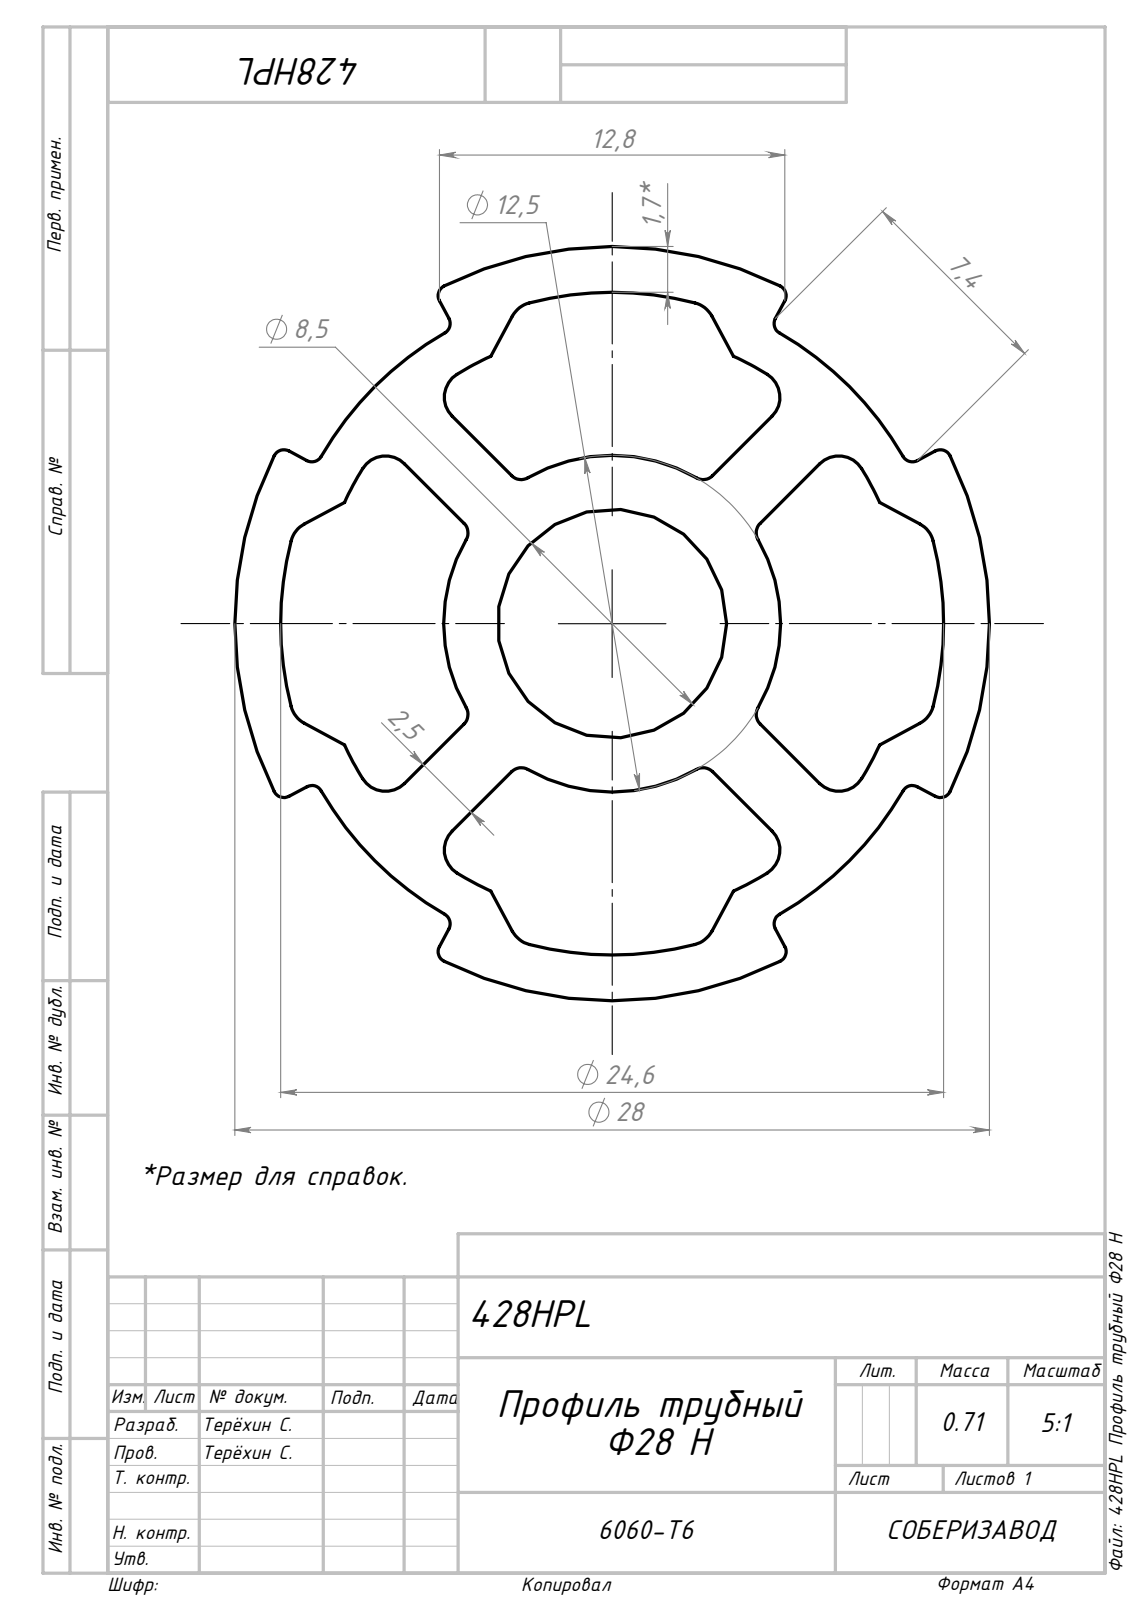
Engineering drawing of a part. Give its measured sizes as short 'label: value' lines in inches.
name: 428HPL Профиль трубный Φ28 H
written by: SolidWorks 2022 (AUTOMOTIVE_DESIGN)
unit: in
bodies: 1 solid, 103 faces (26 planar, 77 cylindrical, 0 other)
size: 39.37 × 1.102 × 1.102
volume: 16.13 in³; area: 384.8 in²
holes: 1× ⌀0.335
rounds: 16× R0.016, 16× R0.039, 8× R0.02, 1× R0.246, 1× R0.429, 1× R0.484, 1× R0.49, 1× R0.551
face distances: 0.098, 0.682, 39.37
